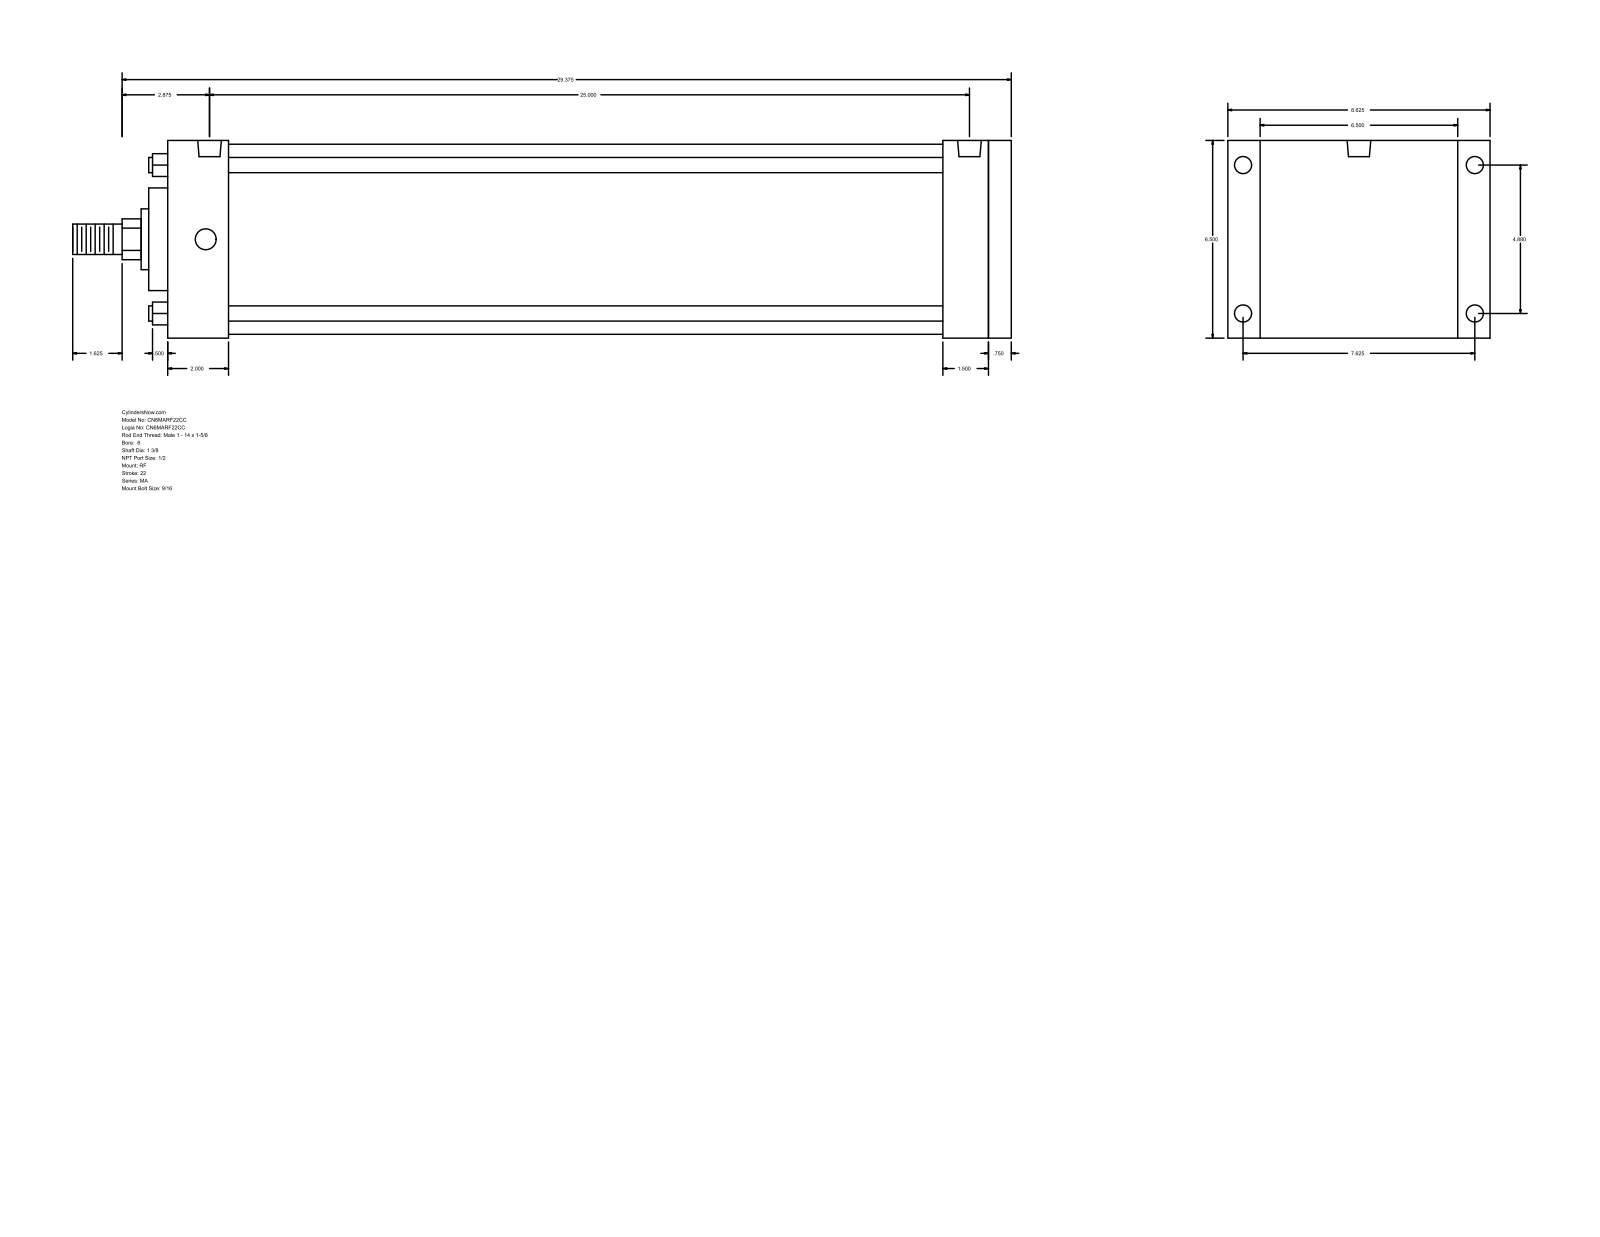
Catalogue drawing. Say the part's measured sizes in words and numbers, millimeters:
The part is named "MA_RF__0600_1.375". Its 3-D file was written by "GSSL Pune (CONFIG_CONTROL_DESIGN)". It is 0 solids with 94 faces: 65 planar, 29 cylindrical and 0 other. Overall it measures 787.4 by 219.07 by 165.1 millimeters. Round holes: 4 of diameter 14.29, 4 of diameter 17.46, 2 of diameter 19.77. Round bosses or shafts: 4 of diameter 12.7, 1 of diameter 158.75, 1 of diameter 85.72, 1 of diameter 50.8, 1 of diameter 34.92, 1 of diameter 25.4. Partial cylindrical surfaces (rounded edges, fillets, slot ends): 1 of radius 17.06. The main face-to-face distances are 165.1, 708.02, 688.98, 19.04, 38.1, 50.8, 638.18, 657.22, 650.88, 600.08. The hole center spacings are 123.96, 193.68, 229.95, 638.17, 3.18, 634.99.
